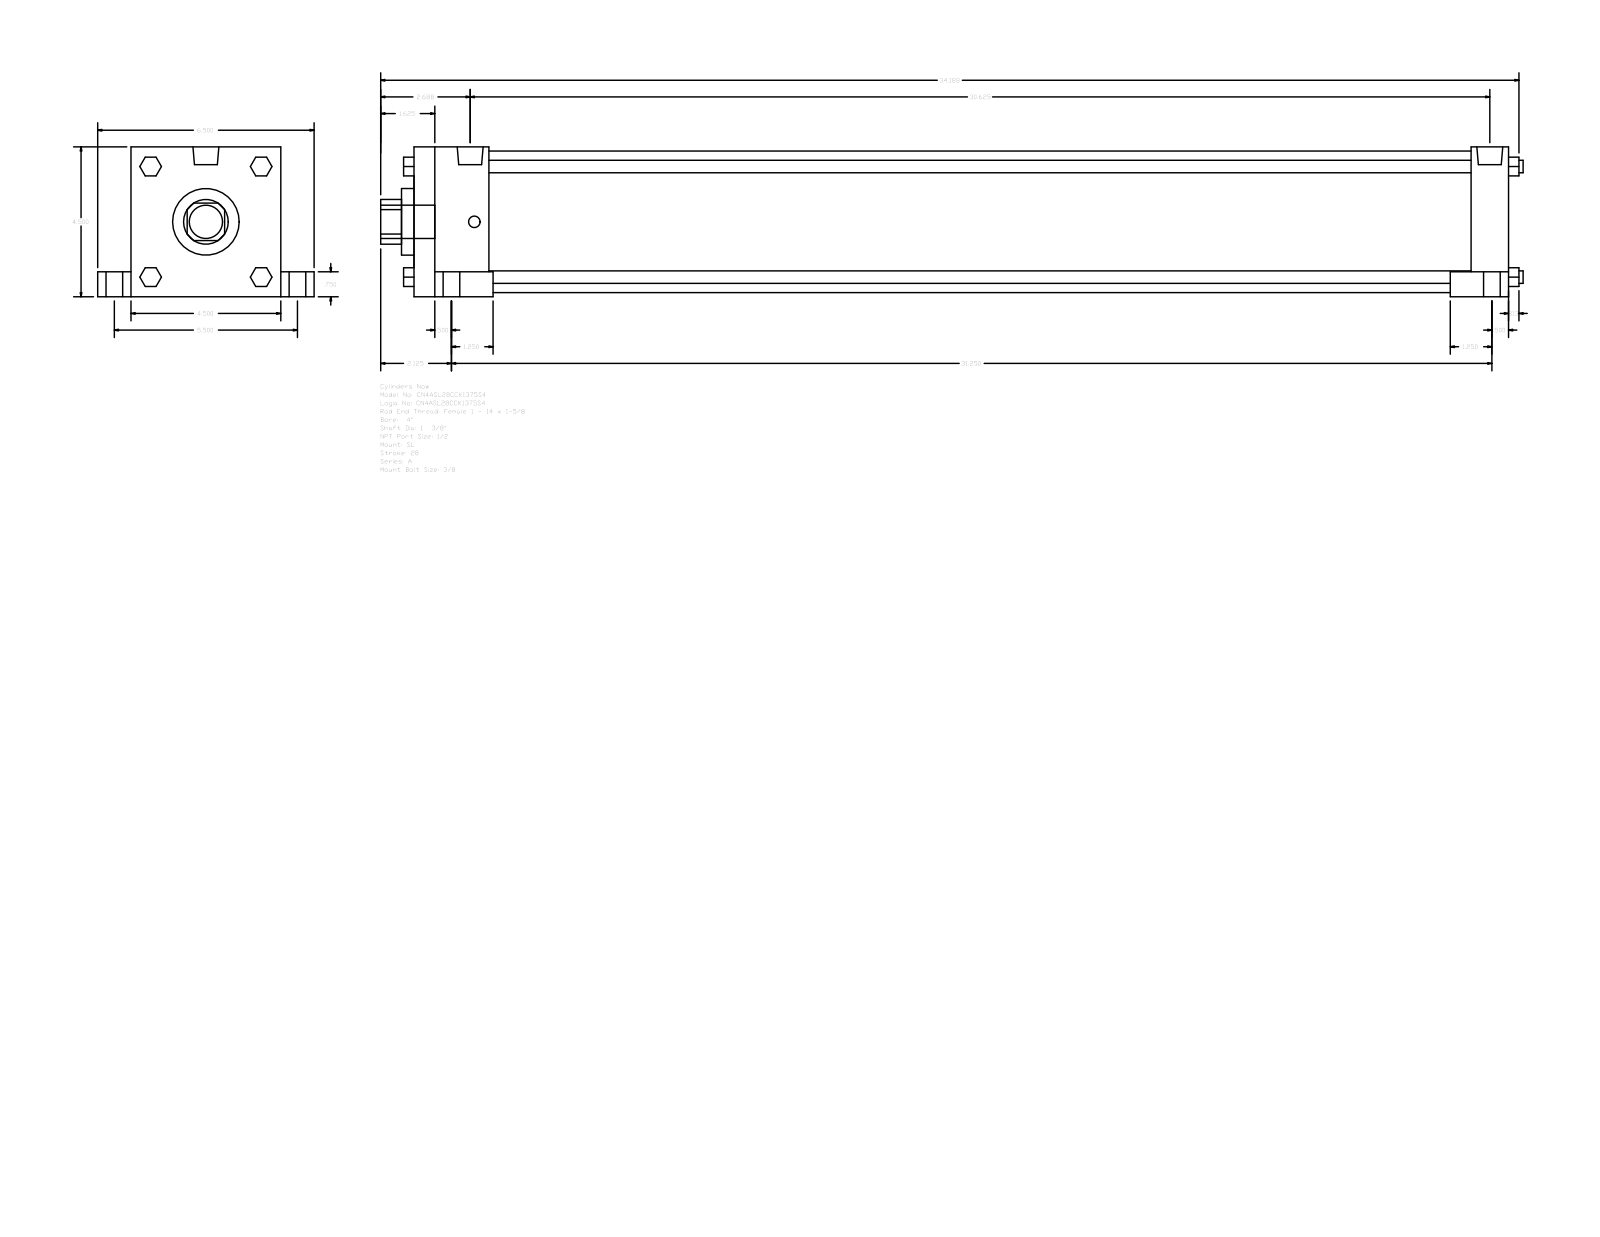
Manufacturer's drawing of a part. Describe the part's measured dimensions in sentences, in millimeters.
The part is named "A_SL__0400_1.375". Its 3-D file was written by "GSSL Pune (CONFIG_CONTROL_DESIGN)". It is 0 solids with 150 faces: 114 planar, 36 cylindrical and 0 other. Overall it measures 871.54 by 165.1 by 114.3 millimeters. Round holes: 1 of diameter 34.92, 1 of diameter 50.8, 1 of diameter 107.95. Round bosses or shafts: 4 of diameter 19.05, 4 of diameter 12.7, 4 of diameter 9.53, 4 of diameter 8.73, 2 of diameter 19.77, 1 of diameter 25.4. Partial cylindrical surfaces (rounded edges, fillets, slot ends): 1 of radius 17.06. The main face-to-face distances are 114.3, 835.02, 28.57, 25.4, 57.15, 777.87, 806.45, 749.3, 139.7, 19.05.
